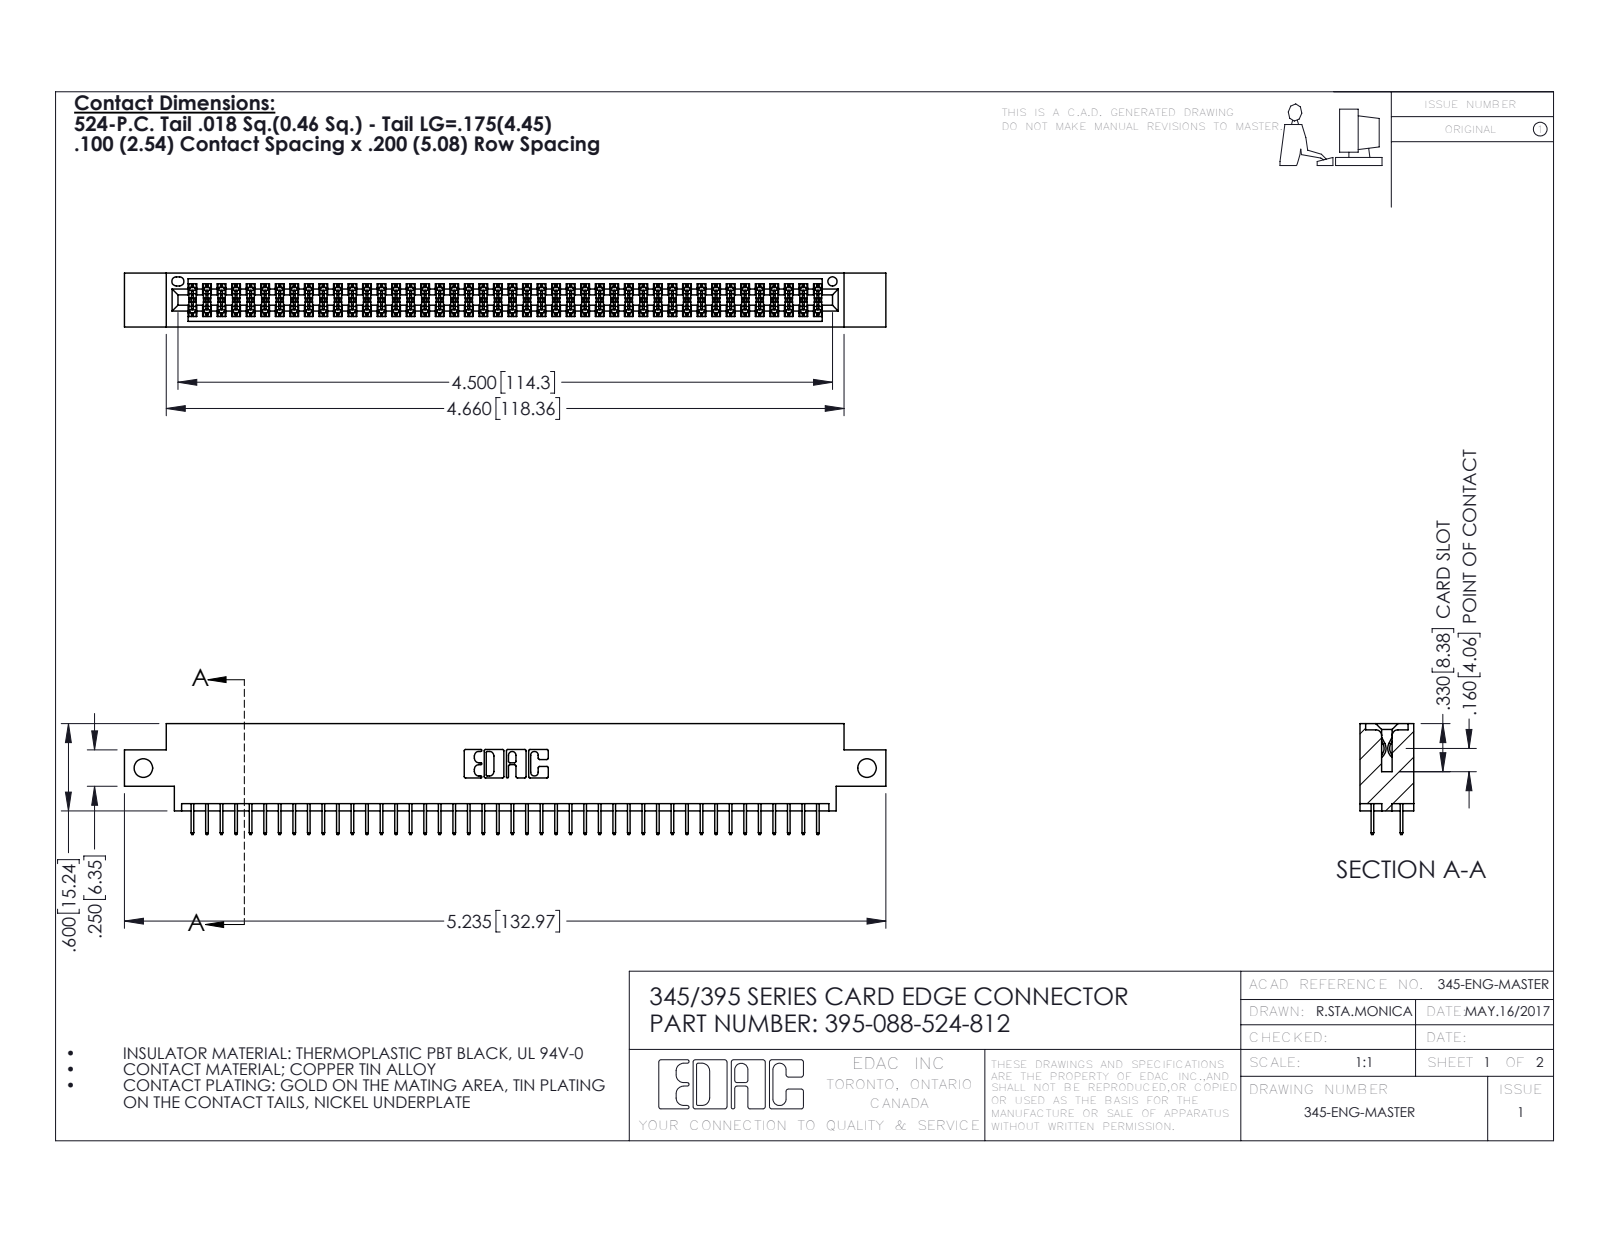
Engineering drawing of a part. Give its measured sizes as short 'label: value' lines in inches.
name: 345-292-001_345-293-124; 345 Part_0.170 Offset - Side Mount; 395-088-524-812
written by: SolidWorks 2016 (CONFIG_CONTROL_DESIGN)
unit: in
bodies: 89 solids, 4882 faces (3516 planar, 1366 cylindrical, 0 other)
size: 5.235 × 0.762 × 0.37
volume: 0.769 in³; area: 28.4 in²
holes: 2× ⌀0.128, 1× ⌀0.064
rounds: 132× R0.006, 22× R0.01, 6× R0.007, 6× R0.031, 3× R0.026, 2× R0.014, 2× R0.019, 2× R0.022
face distances: 0.072, 0.298, 0.37, 0.2, 0.098, 0.272, 0.025, 0.225, 0.175, 0.072
hole spacings: 4.975
